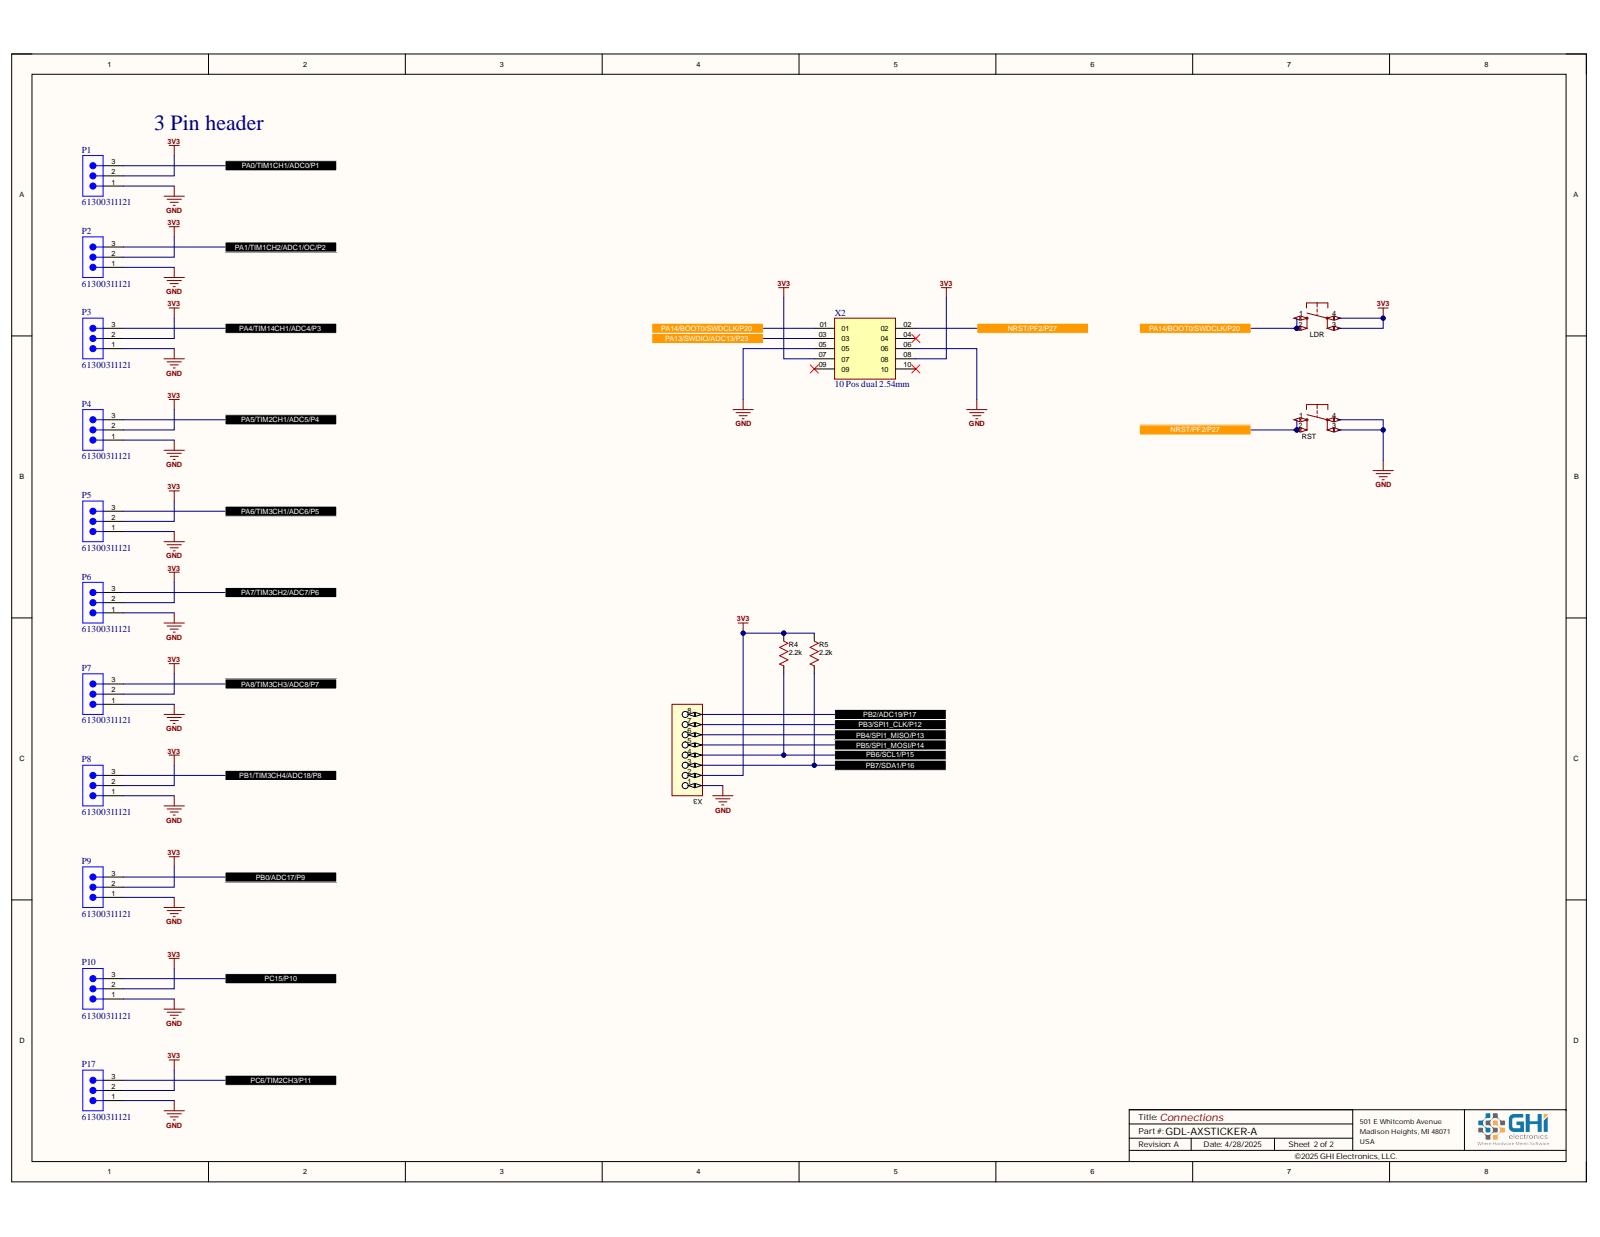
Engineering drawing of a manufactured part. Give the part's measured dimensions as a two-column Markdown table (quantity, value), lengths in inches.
| quantity | value |
| --- | --- |
| part name | PCB; Board; P10; 61300311121 (+7 more) |
| STEP written by | Open CASCADE 7.5 (AUTOMOTIVE_DESIGN) |
| units | inches |
| bodies | 210 solids, 7939 faces (5636 planar, 1875 cylindrical, 428 other) |
| overall size | 2.047 × 1.457 × 0.645 |
| volume | 0.162 in³ |
| surface area | 19.74 in² |
| round holes (diameter × count) | 0.043 × 33, 0.035 × 24, 0.012 × 12, 0.02 × 6, 0.118 × 4, 0.026 × 2 |
| round bosses / shafts (diameter × count) | 0.02 × 2 |
| partial cylindrical surfaces (radius × count) | 0.006 × 116, 0.004 × 99, 0.008 × 86, 0.008 × 52, 0.005 × 37, 0.013 × 24, 0.016 × 24, 0.026 × 24 |
| main face-to-face distances | 0.1, 0.4, 0.098, 0.021, 0.2, 0.4, 0.078, 0.057, 0.478, 0.362 |
| hole center spacings | 0.1, 0.224, 0.141, 0.2, 0.316, 0.412, 0.3, 0.4 |
